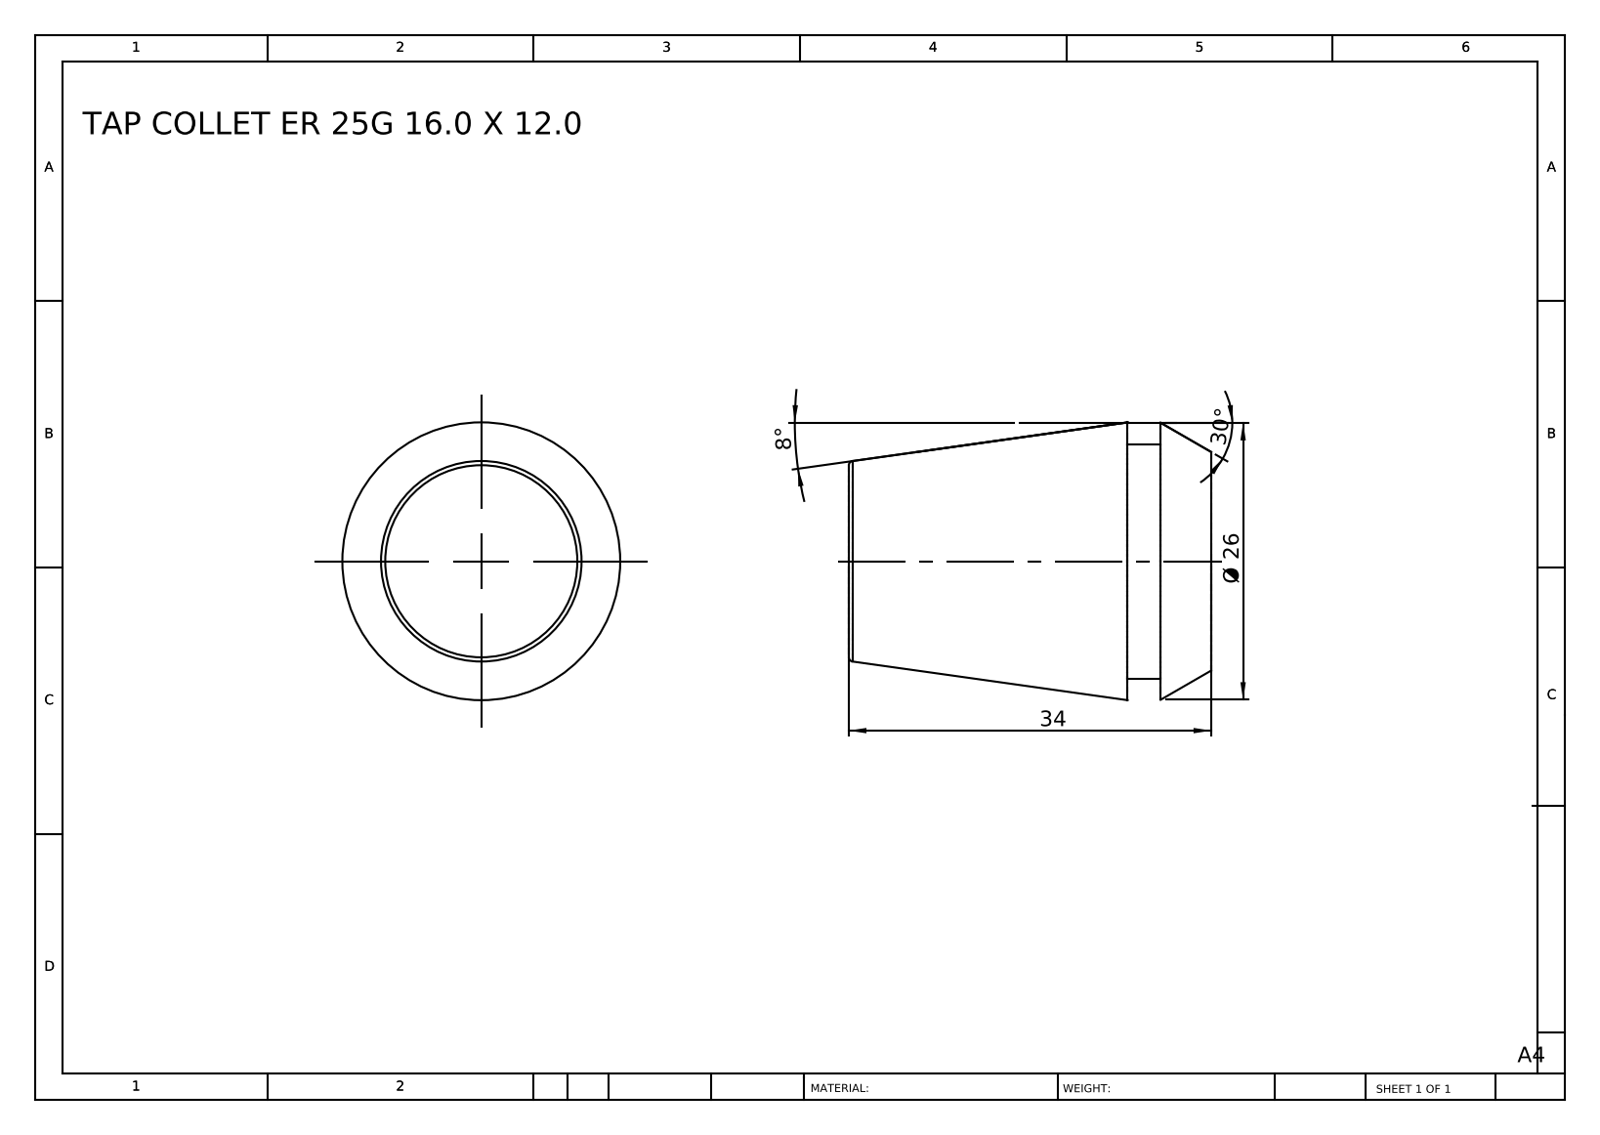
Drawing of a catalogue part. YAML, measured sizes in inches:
part_name: "TAP COLLET ER 25G 16.0 X 12.0"
step_written_by: "SolidWorks 2014 (CONFIG_CONTROL_DESIGN)"
units: inches
bodies: {solids: 1, faces: 12, planar: 4, cylindrical: 2, other: 6}
overall_size: [1.339, 1.026, 1.026]
volume: 0.83
surface_area: 5.233
round_bosses_or_shafts:
  - {diameter: 0.866, count: 1}
face_to_face_distances: [1.339, 0.309, 1.03, 0.187, 0.122, 1.152]
